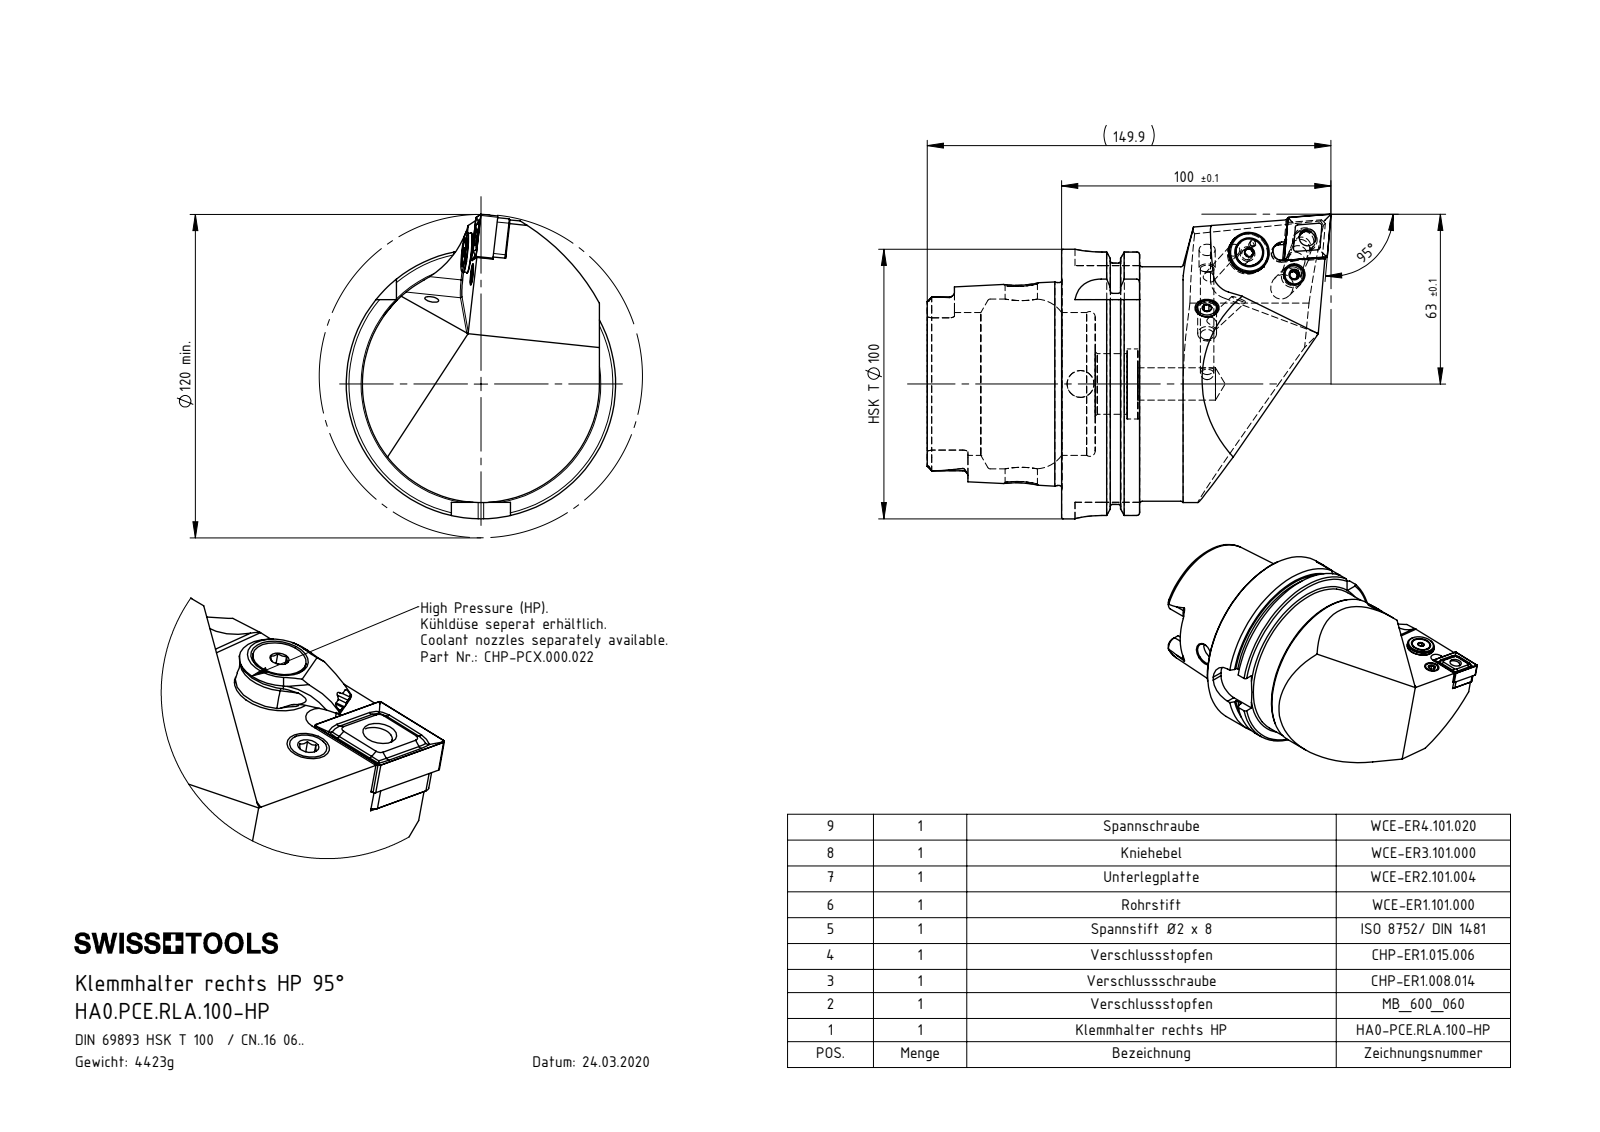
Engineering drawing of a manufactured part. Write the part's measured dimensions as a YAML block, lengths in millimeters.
part_name: "WCE-ER1.101.000; DIN 7991 - M5x15; CHP-ER1.008.014_A; WCE-ER2.101.004_A (+8 more)"
step_written_by: "SolidWorks 2017 (AUTOMOTIVE_DESIGN)"
units: millimeters
bodies: {solids: 13, faces: 386, planar: 159, cylindrical: 93, other: 134}
overall_size: [149.9, 113, 100]
volume: 561929
surface_area: 75905
round_holes:
  - {diameter: 5, count: 3}
  - {diameter: 4.2, count: 2}
  - {diameter: 7, count: 2}
  - {diameter: 12, count: 2}
  - {diameter: 1.2, count: 1}
  - {diameter: 2, count: 1}
  - {diameter: 2.5, count: 1}
  - {diameter: 3, count: 1}
  - {diameter: 5.2, count: 1}
  - {diameter: 6.35, count: 1}
  - {diameter: 8.05, count: 1}
  - {diameter: 8.4, count: 1}
round_bosses_or_shafts:
  - {diameter: 8, count: 2}
  - {diameter: 6, count: 2}
  - {diameter: 100, count: 1}
  - {diameter: 91.95, count: 1}
  - {diameter: 87, count: 1}
  - {diameter: 75.26, count: 1}
  - {diameter: 15, count: 1}
  - {diameter: 13.4, count: 1}
partial_cylinders:
  - {radius: 1.9, count: 6}
  - {radius: 0.4, count: 4}
  - {radius: 1.5, count: 4}
  - {radius: 3.5, count: 4}
  - {radius: 10, count: 4}
  - {radius: 0.3, count: 2}
  - {radius: 0.5, count: 2}
  - {radius: 4.83, count: 2}
face_to_face_distances: [12.45, 28.95, 16.5, 49.9, 62.35, 78.85, 87.8, 78.2, 28.3, 15.85]
hole_center_spacings: [19.18, 4.49, 4.5, 4.51, 4.52, 14.75, 14.99, 18.76]
